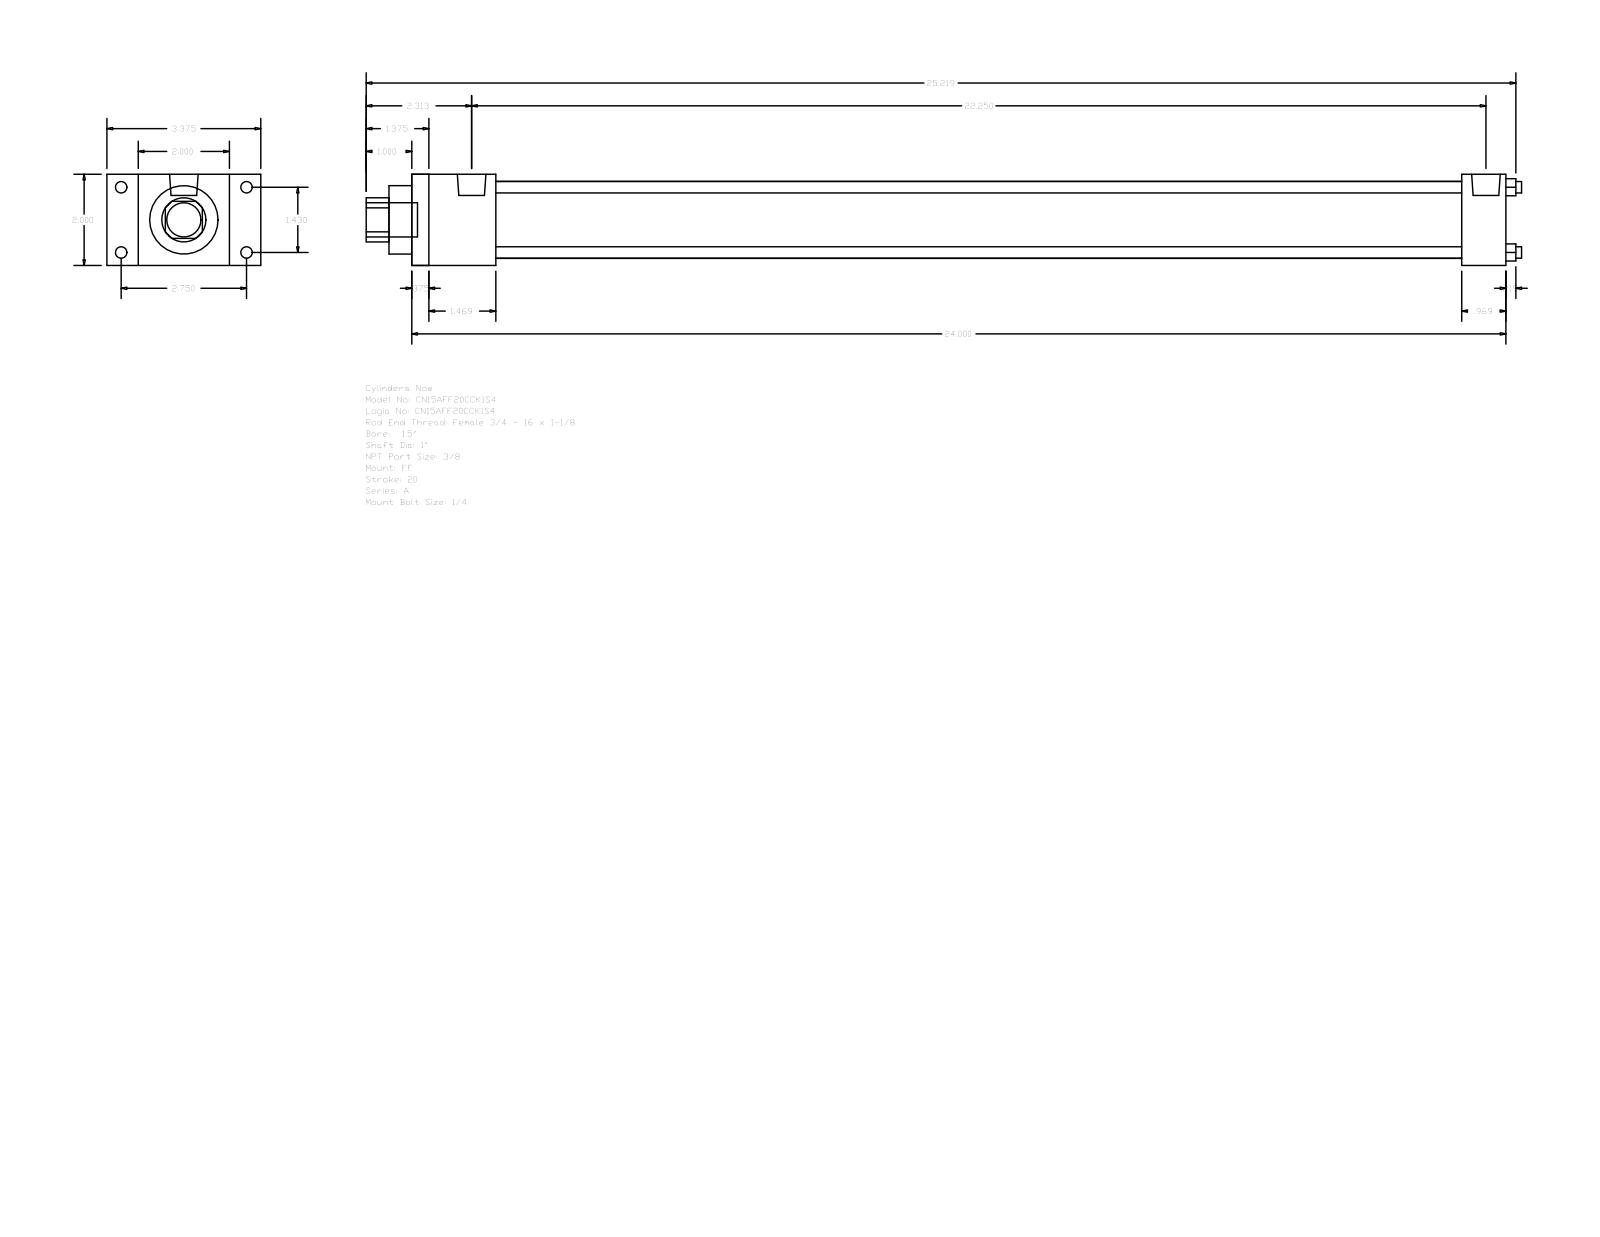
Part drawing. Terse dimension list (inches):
name: A_FF__0150_1
written by: GSSL Pune (CONFIG_CONTROL_DESIGN)
unit: in
bodies: 0 solids, 92 faces (64 planar, 28 cylindrical, 0 other)
size: 25.344 × 3.375 × 2
holes: 4× ⌀0.25, 1× ⌀1, 1× ⌀1.5, 1× ⌀1.69
bosses: 4× ⌀0.25, 4× ⌀0.219, 2× ⌀0.627, 1× ⌀0.75
rounds: 1× R0.484
face distances: 2, 24, 0.375, 23.625, 1.844, 23.031, 1.469, 22.656, 21.187, 22.156
hole spacings: 1.011, 1.43, 2.022
